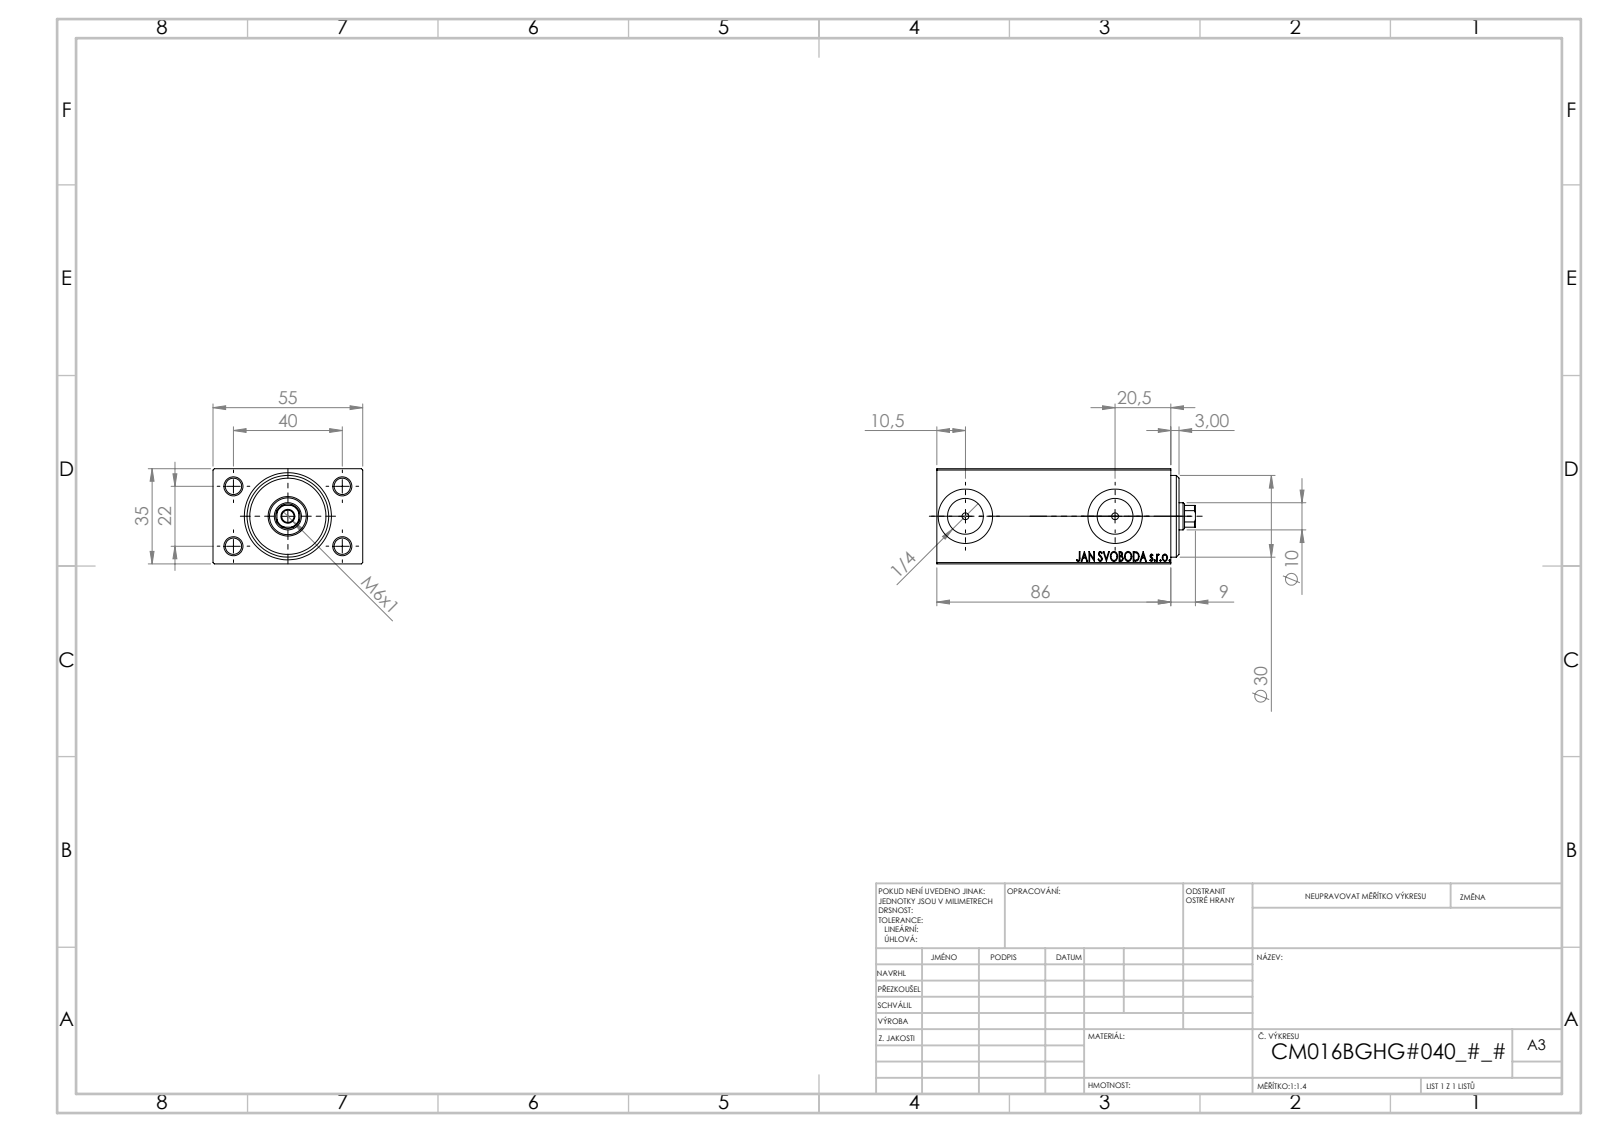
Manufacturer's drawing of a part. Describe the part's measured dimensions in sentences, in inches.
The part is named "V450CM_VC_B; V450CM_B_VCP; V450CM_B_Body". Its 3-D file was written by "SolidWorks 2019 (CONFIG_CONTROL_DESIGN)". It is 3 solids with 881 faces: 401 planar, 54 cylindrical and 426 other. Overall it measures 3.74 by 2.165 by 1.378 inches. Its volume is 9.559 cubic inches and its surface area 50.91 square inches. Round holes: 4 of diameter 0.236, 2 of diameter 0.098, 2 of diameter 0.518, 2 of diameter 0.787, 1 of diameter 0.177, 1 of diameter 0.394, 1 of diameter 0.531, 1 of diameter 0.571, 1 of diameter 0.63, 1 of diameter 0.709, 1 of diameter 1.181. Partial cylindrical surfaces (rounded edges, fillets, slot ends): 1 of radius 0.177. The main face-to-face distances are 1.378, 2.165, 0.197, 3.189, 3.386, 0.315, 0.118, 3.504, 3.307, 2.992. The hole center spacings are 0.899, 0.866, 1.575, 1.797, 2.165.
